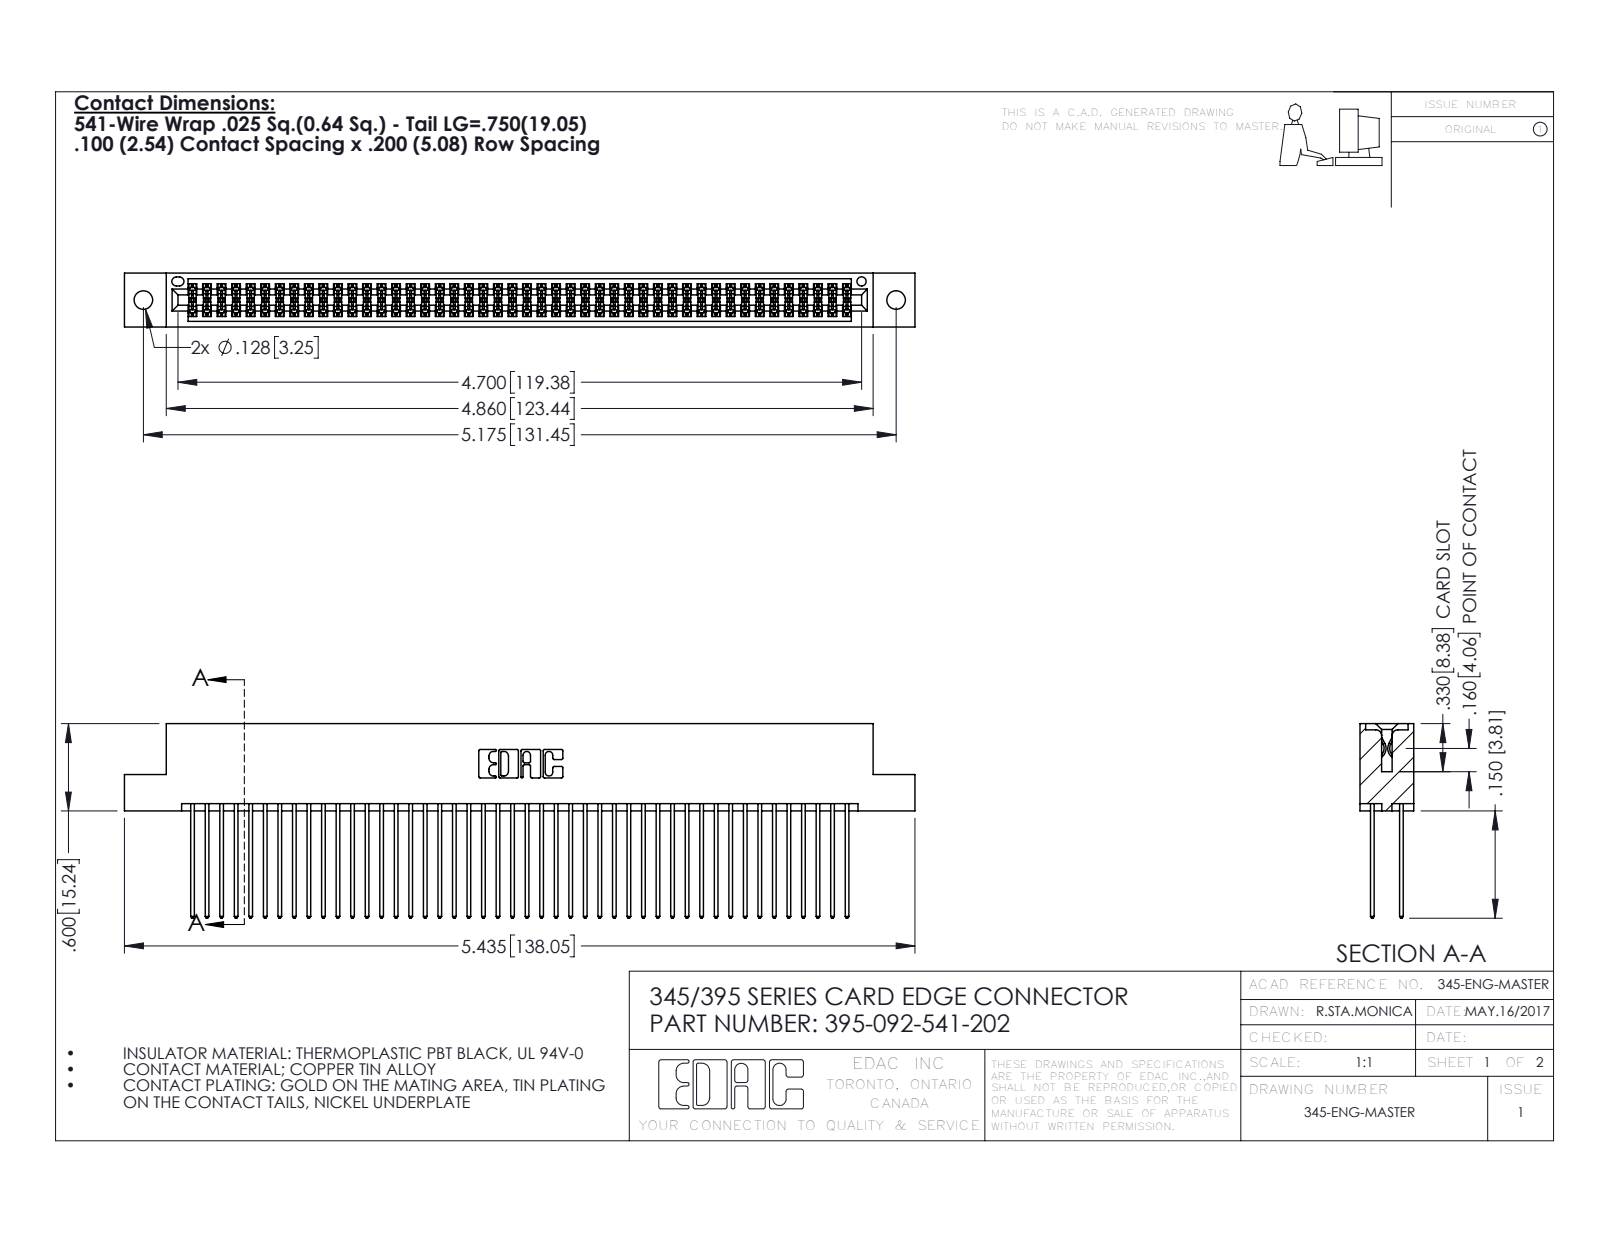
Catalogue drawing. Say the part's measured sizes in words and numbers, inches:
The part is named "345 Part_Flush Mounting Lugs - 0.128 Dia; 345-292-001_345-293-141; 395-092-541-202". Its 3-D file was written by "SolidWorks 2016 (CONFIG_CONTROL_DESIGN)". It is 93 solids with 4726 faces: 3116 planar, 1610 cylindrical and 0 other. Overall it measures 5.435 by 1.337 by 0.37 inches. Its volume is 0.851 cubic inches and its surface area 35.48 square inches. Round holes: 2 of diameter 0.128, 1 of diameter 0.064. Partial cylindrical surfaces (rounded edges, fillets, slot ends): 138 of radius 0.006, 92 of radius 0.01, 22 of radius 0.01, 6 of radius 0.007, 6 of radius 0.031, 3 of radius 0.026, 2 of radius 0.014, 2 of radius 0.019. The main face-to-face distances are 0.298, 0.072, 0.2, 0.098, 0.272, 0.025, 0.225, 0.37, 0.175, 0.149. The hole center spacings are 0.27, 4.939, 5.175.
